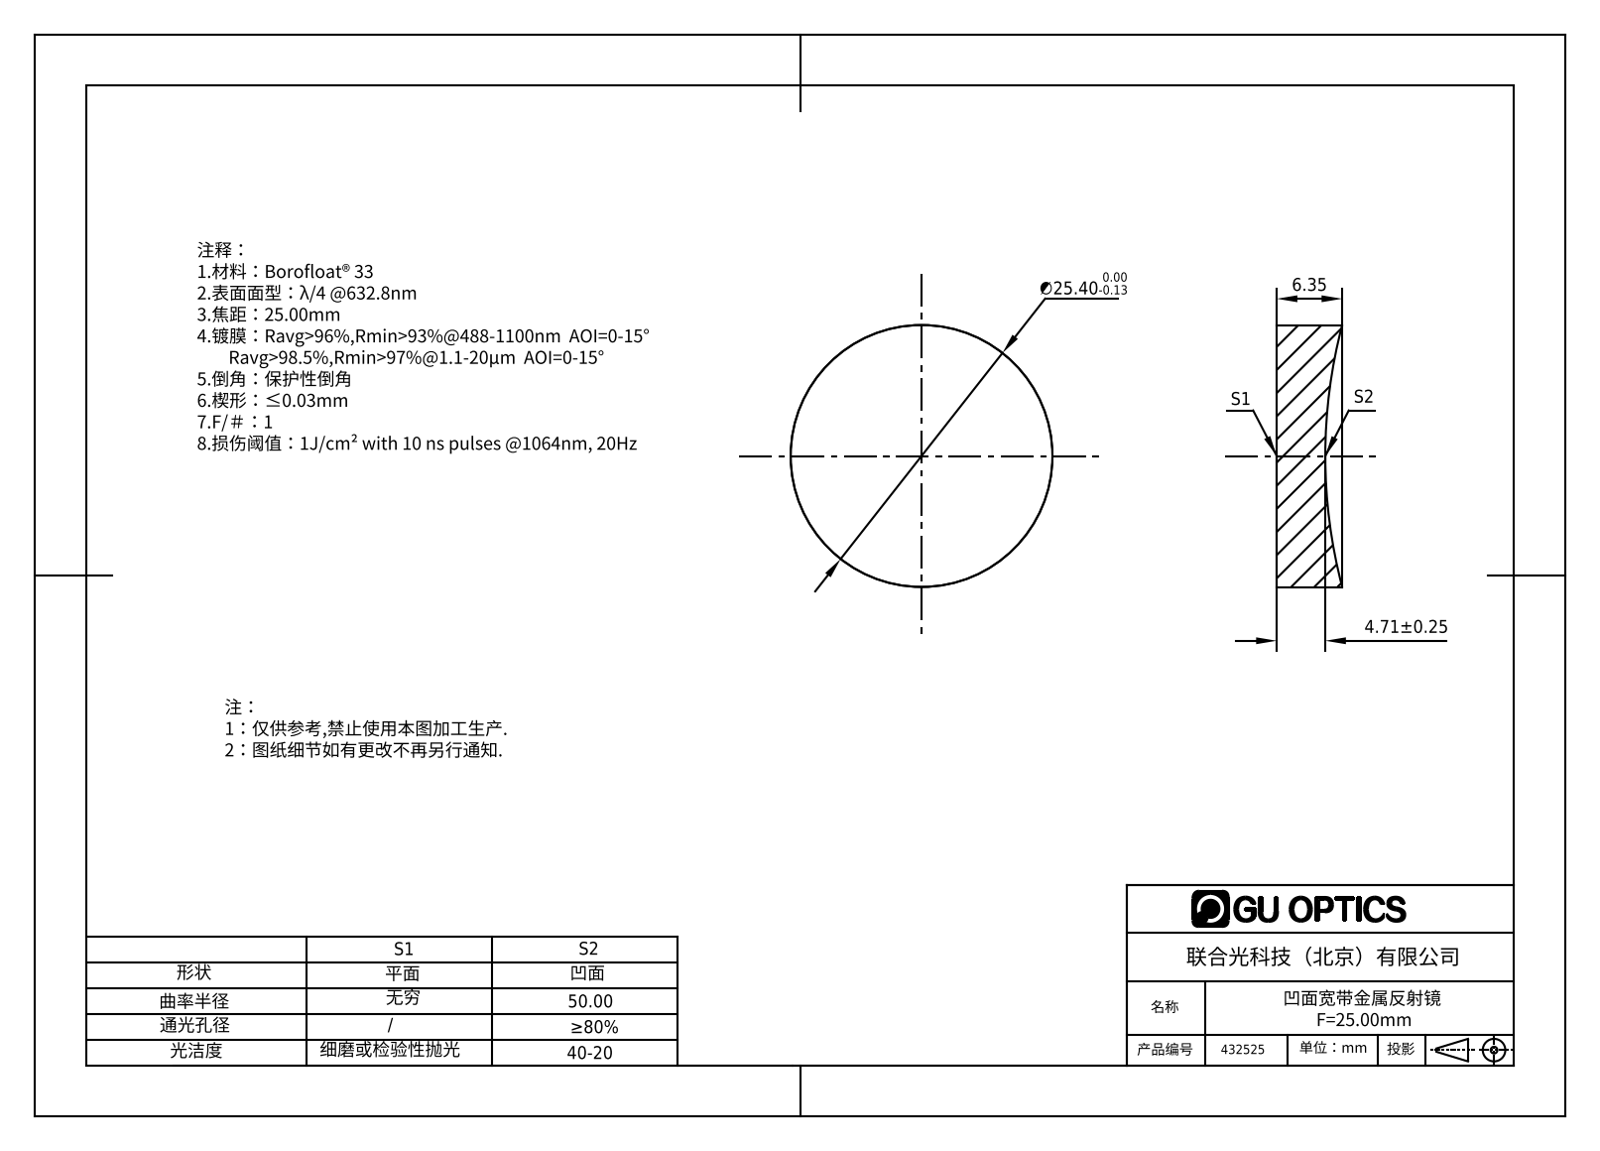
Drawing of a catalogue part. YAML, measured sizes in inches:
part_name: "432515"
step_written_by: "SolidWorks 2016 (AUTOMOTIVE_DESIGN)"
units: inches
bodies: {solids: 1, faces: 5, planar: 1, cylindrical: 2, other: 2}
overall_size: [1, 1, 0.25]
volume: 0.171
surface_area: 2.37
round_bosses_or_shafts:
  - {diameter: 1, count: 1}
